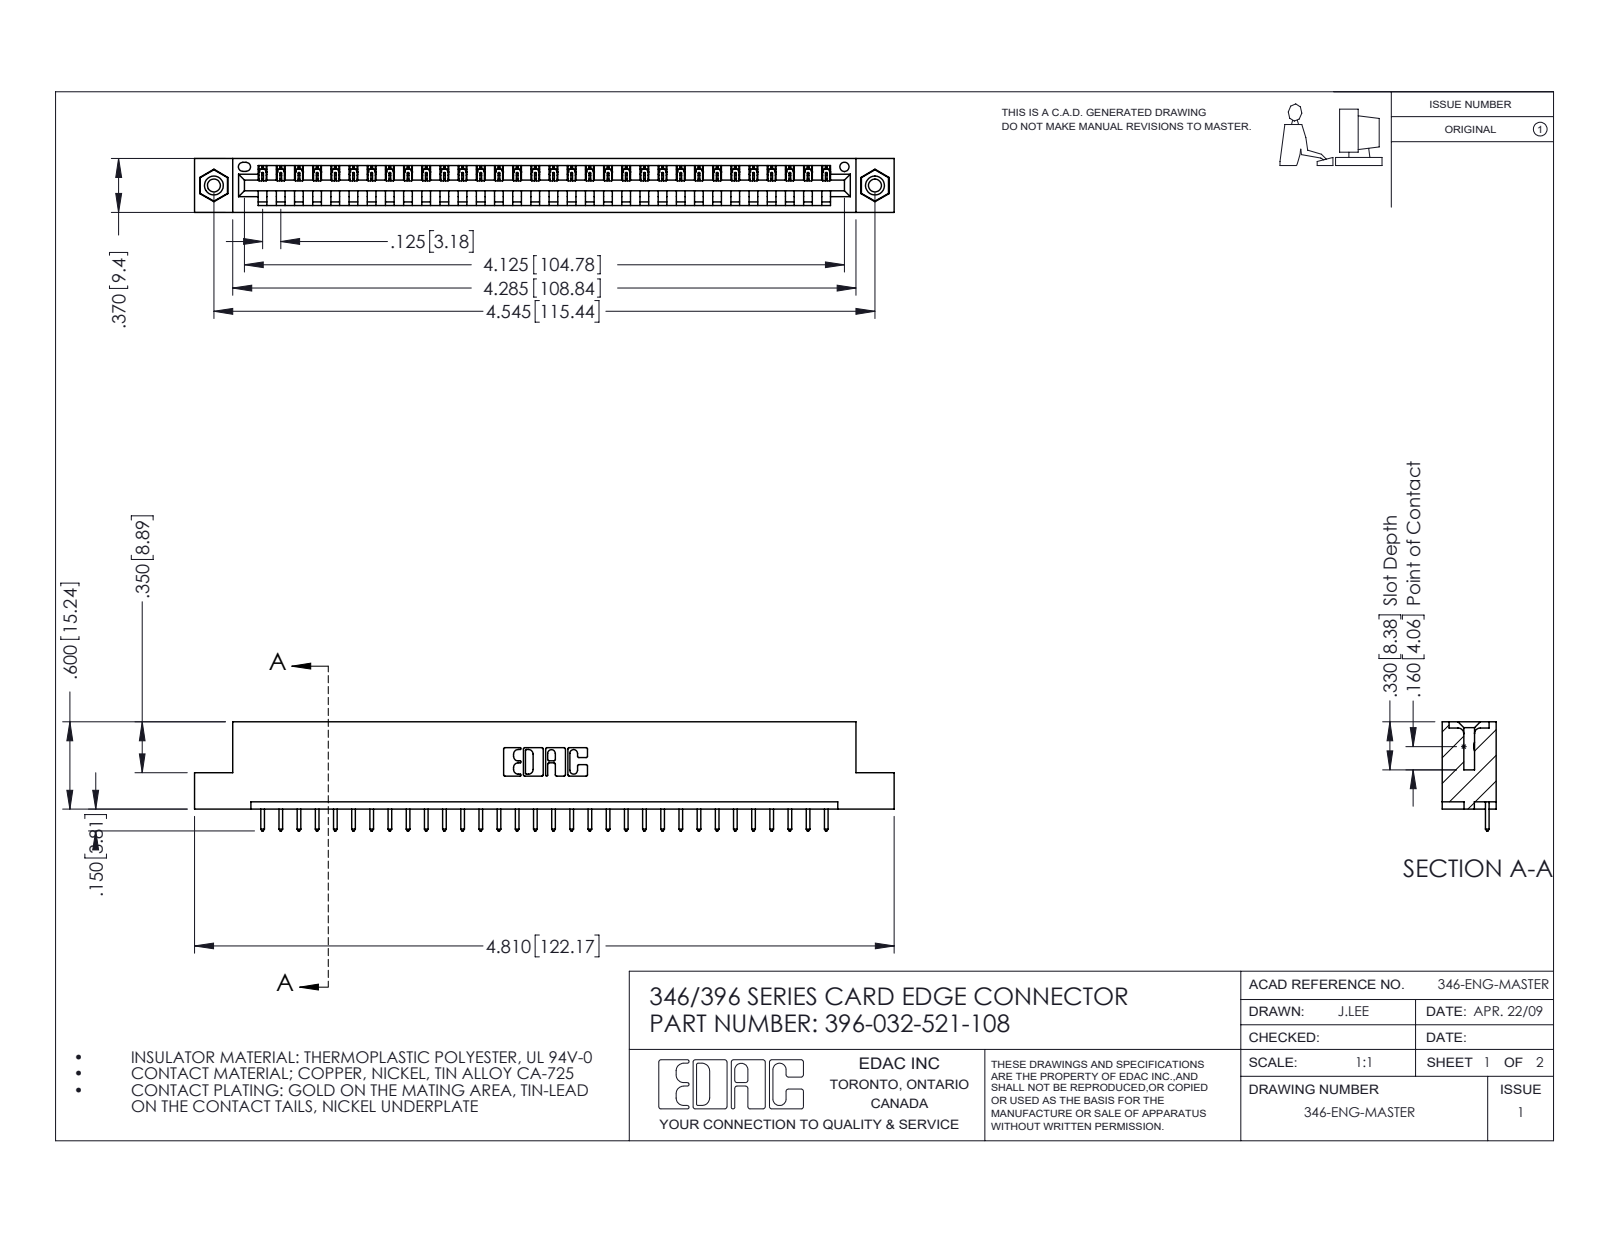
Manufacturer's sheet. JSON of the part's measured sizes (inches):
{"part_name": "345-292-001_345-293-121; 396-032-521-108; 346 Part_Flush Mounting Lugs - 0.156 Dia-TI; 345-250-001_345-250-003-102", "step_written_by": "SolidWorks 2016 (CONFIG_CONTROL_DESIGN)", "units": "inches", "bodies": {"solids": 35, "faces": 2038, "planar": 1388, "cylindrical": 634, "other": 16}, "overall_size": [4.81, 0.75, 0.37], "volume_in3": 0.704, "surface_area_in2": 21.64, "round_holes": [[0.089, 2], [0.125, 2], [0.156, 2], [0.064, 1]], "round_bosses_or_shafts": [[0.155, 2]], "partial_cylinders_radius": [[0.006, 64], [0.01, 64], [0.01, 22], [0.007, 6], [0.031, 6], [0.026, 3], [0.031, 2], [0.04, 2]], "face_to_face_distances": [0.048, 0.322, 0.37, 0.25, 0.072, 0.298, 0.025, 0.148, 0.222, 0.1], "hole_center_spacings": [0.246, 4.337, 4.545]}
